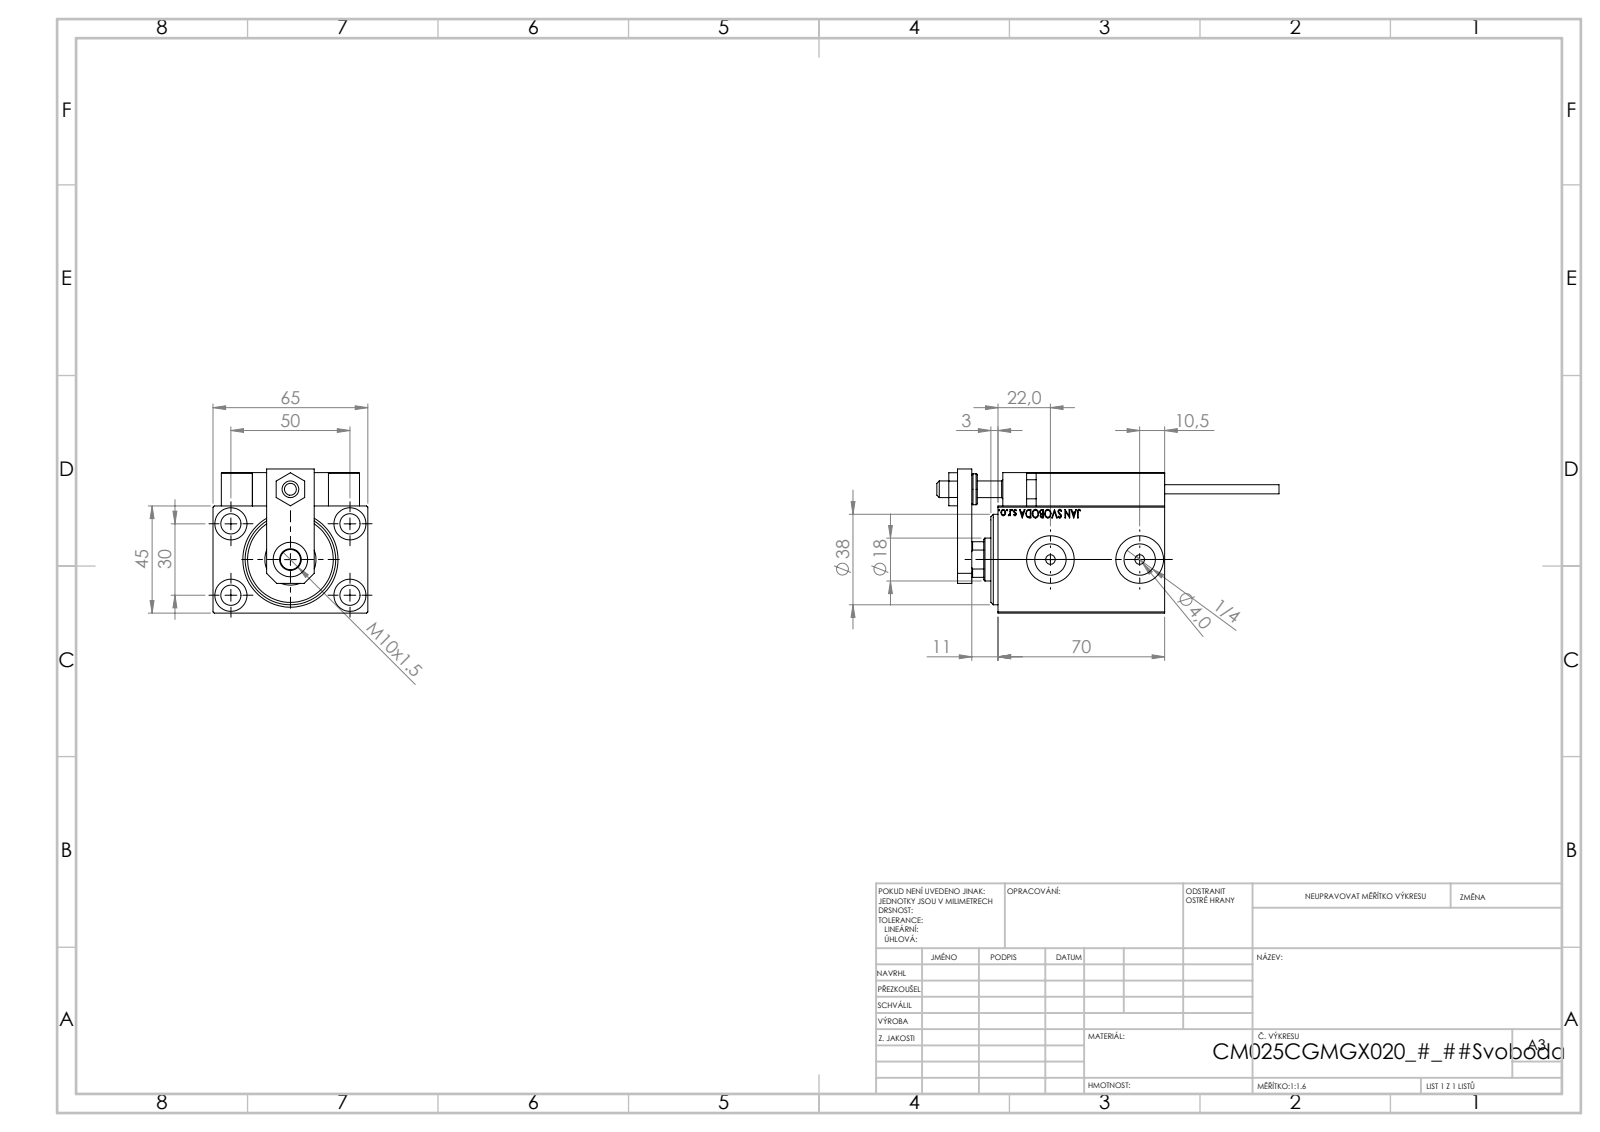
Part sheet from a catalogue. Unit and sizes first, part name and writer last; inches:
Units: inches
Overall size (bounding box): 5.657 × 2.559 × 2.382
Round holes (diameter × count): ⌀0.157 ×6, ⌀0.315 ×5, ⌀0.335 ×5, ⌀0.126 ×4, ⌀0.531 ×4, ⌀0.197 ×2, ⌀0.518 ×2, ⌀0.787 ×2, ⌀0.276 ×1, ⌀0.571 ×1, ⌀0.709 ×1, ⌀0.846 ×1
Round bosses / shafts (diameter × count): ⌀0.197 ×2, ⌀0.15 ×2, ⌀0.512 ×1, ⌀0.433 ×1
Partial cylindrical surfaces — rounded edges, fillets, slot ends (radius × count): R0.012 ×30, R0.118 ×2, R0.335 ×1
Main face-to-face distances: 1.772, 2.323, 0.551, 2.559, 0.236, 0.118, 0.748, 0.197, 0.276, 0.787
Hole centre spacings: 1.148, 0.448, 0.787, 0.87, 1.138, 1.165, 1.169, 1.181
Volume: 13.61 in³ · Surface area: 107.3 in²
Bodies: 23 solids, 1282 faces (560 planar, 188 cylindrical, 534 other)
Part name (STEP PRODUCT): SWITCH X; KONCOVKA; V450CM_C_VCP; V450CM_VC_B (+7 more)
STEP written by: SolidWorks 2019 (CONFIG_CONTROL_DESIGN)
